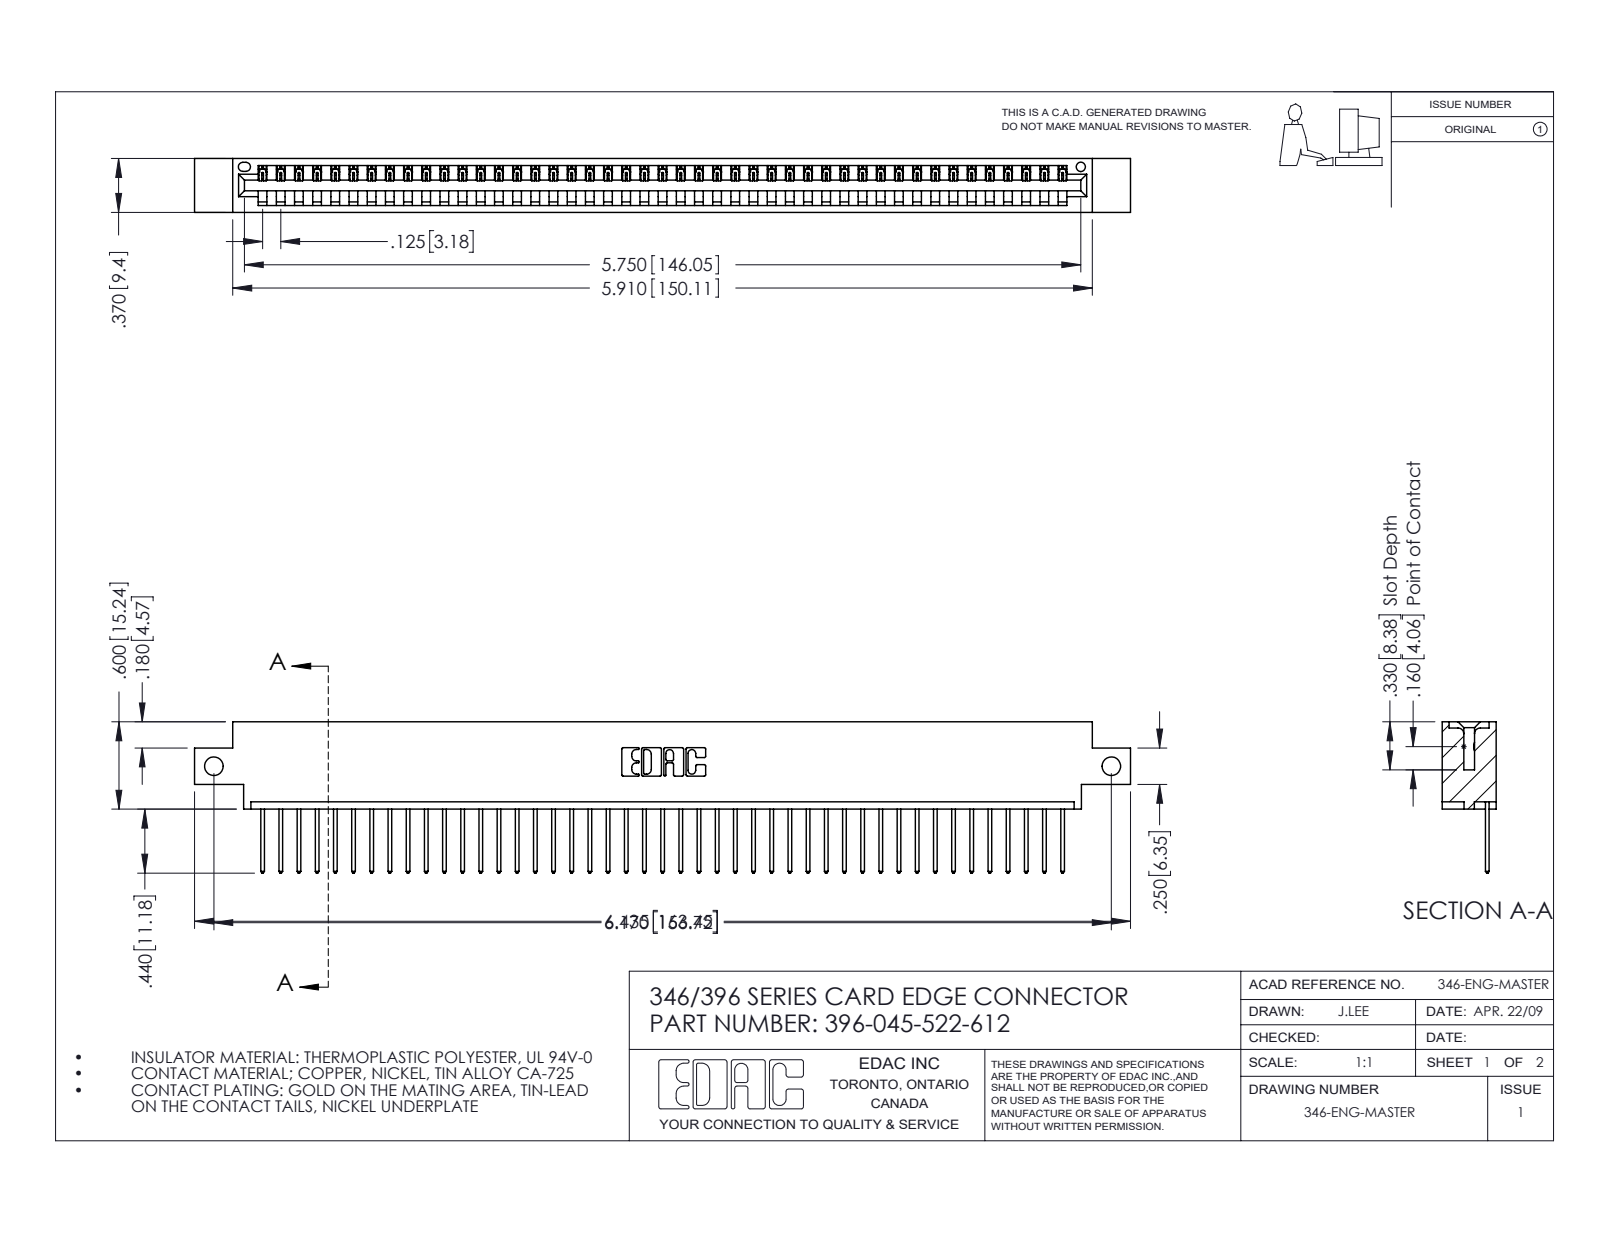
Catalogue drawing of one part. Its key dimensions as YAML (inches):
part_name: "396-045-522-612; 345-292-001_345-293-122; 346 Part_0.170 Offset - Side Mount"
step_written_by: "SolidWorks 2016 (CONFIG_CONTROL_DESIGN)"
units: inches
bodies: {solids: 46, faces: 2736, planar: 1880, cylindrical: 856, other: 0}
overall_size: [6.435, 1.04, 0.37]
volume: 0.942
surface_area: 30.22
round_holes:
  - {diameter: 0.128, count: 2}
  - {diameter: 0.064, count: 1}
partial_cylinders:
  - {radius: 0.006, count: 90}
  - {radius: 0.01, count: 90}
  - {radius: 0.01, count: 22}
  - {radius: 0.007, count: 6}
  - {radius: 0.031, count: 6}
  - {radius: 0.026, count: 3}
  - {radius: 0.031, count: 2}
  - {radius: 0.04, count: 2}
face_to_face_distances: [0.048, 0.322, 0.37, 0.25, 0.072, 0.298, 0.025, 0.148, 0.222, 0.1]
hole_center_spacings: [6.17]
